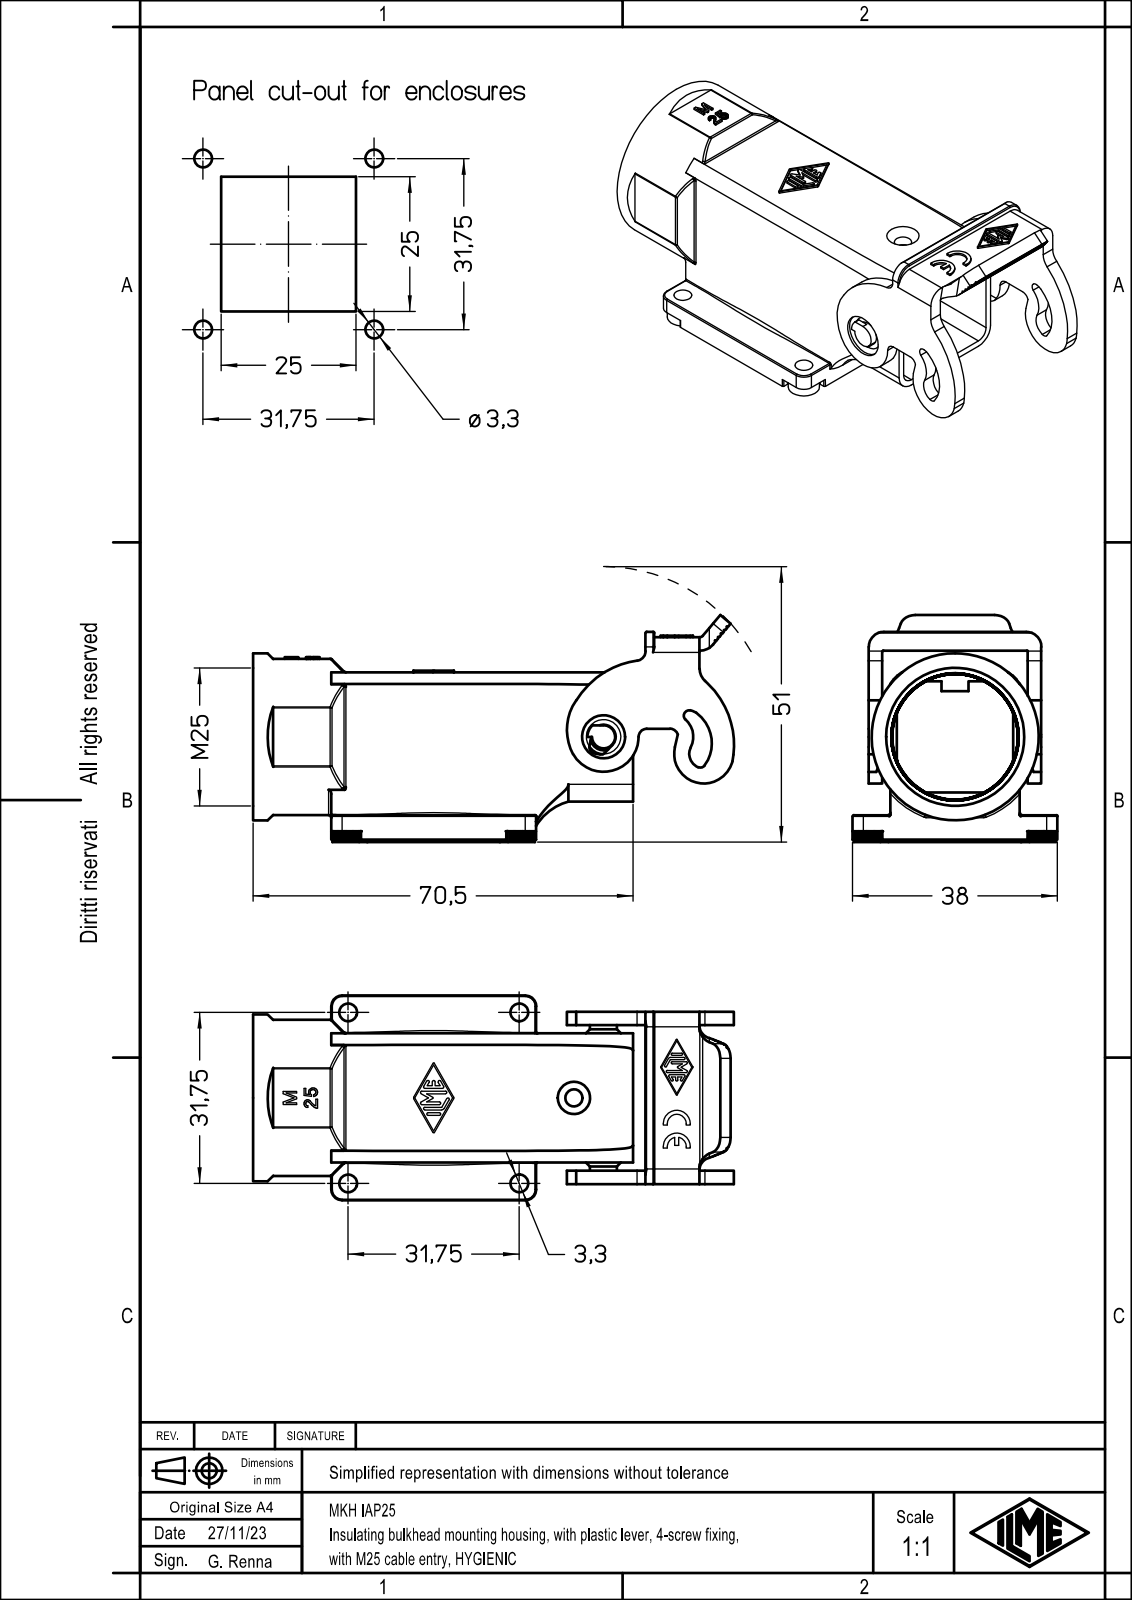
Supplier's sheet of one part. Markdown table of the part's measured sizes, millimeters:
| quantity | value |
| --- | --- |
| part name | MKH IAP25 |
| STEP written by | Creo Elements/Direct Modeling 20.1B 02-Apr-2019 (C) Parametric Technology GmbH (AUTOMOTIVE_DESIGN) |
| units | millimeters |
| bodies | 1 solid, 690 faces (354 planar, 233 cylindrical, 103 other) |
| overall size | 89.2 × 42.14 × 38 |
| volume | 19 134 mm³ |
| surface area | 19 333 mm² |
| round holes (diameter × count) | 3 × 4, 3.3 × 4, 3.2 × 1, 8 × 1, 23.6 × 1 |
| round bosses / shafts (diameter × count) | 31 × 1, 5 × 1, 4.3 × 1 |
| partial cylindrical surfaces (radius × count) | 0.2 × 59, 0.5 × 16, 2 × 16, 0.25 × 15, 3.2 × 11, 0.1 × 7, 2.8 × 6, 0.3 × 4 |
| main face-to-face distances | 1.2, 22.8, 2.5, 24, 28, 4, 1.5, 21.6, 26.8, 29.5 |
| hole center spacings | 31.75, 31.74, 44.78, 44.89, 18.83, 18.84, 44.79, 44.9 |
